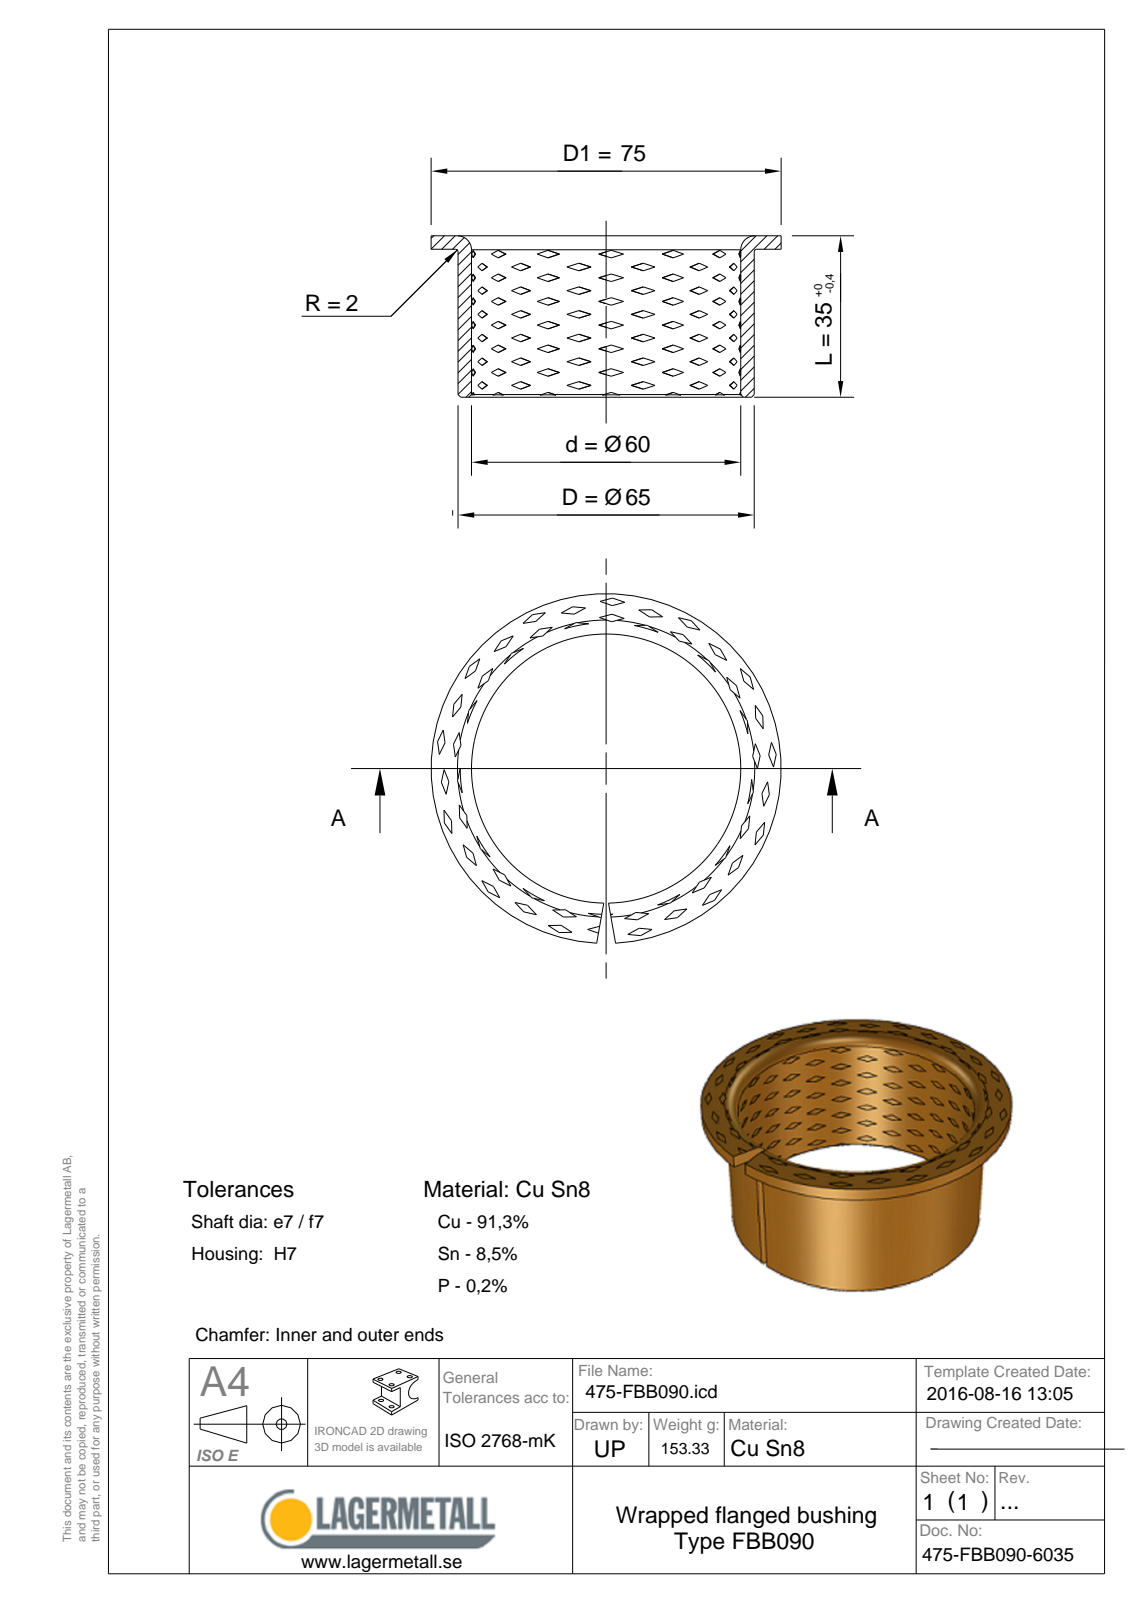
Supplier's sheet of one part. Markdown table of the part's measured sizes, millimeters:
| quantity | value |
| --- | --- |
| part name | 475-FBB090-6035 |
| STEP written by | Spatial InterOp 3D (CONFIG_CONTROL_DESIGN) |
| units | millimeters |
| bodies | 1 solid, 12 faces (5 planar, 3 cylindrical, 4 other) |
| overall size | 75 × 74.96 × 35 |
| volume | 18 930 mm³ |
| surface area | 16 341 mm² |
| round holes (diameter × count) | 60 × 1 |
| round bosses / shafts (diameter × count) | 75 × 1, 65 × 1 |
| main face-to-face distances | 2.5, 32.5, 35 |
